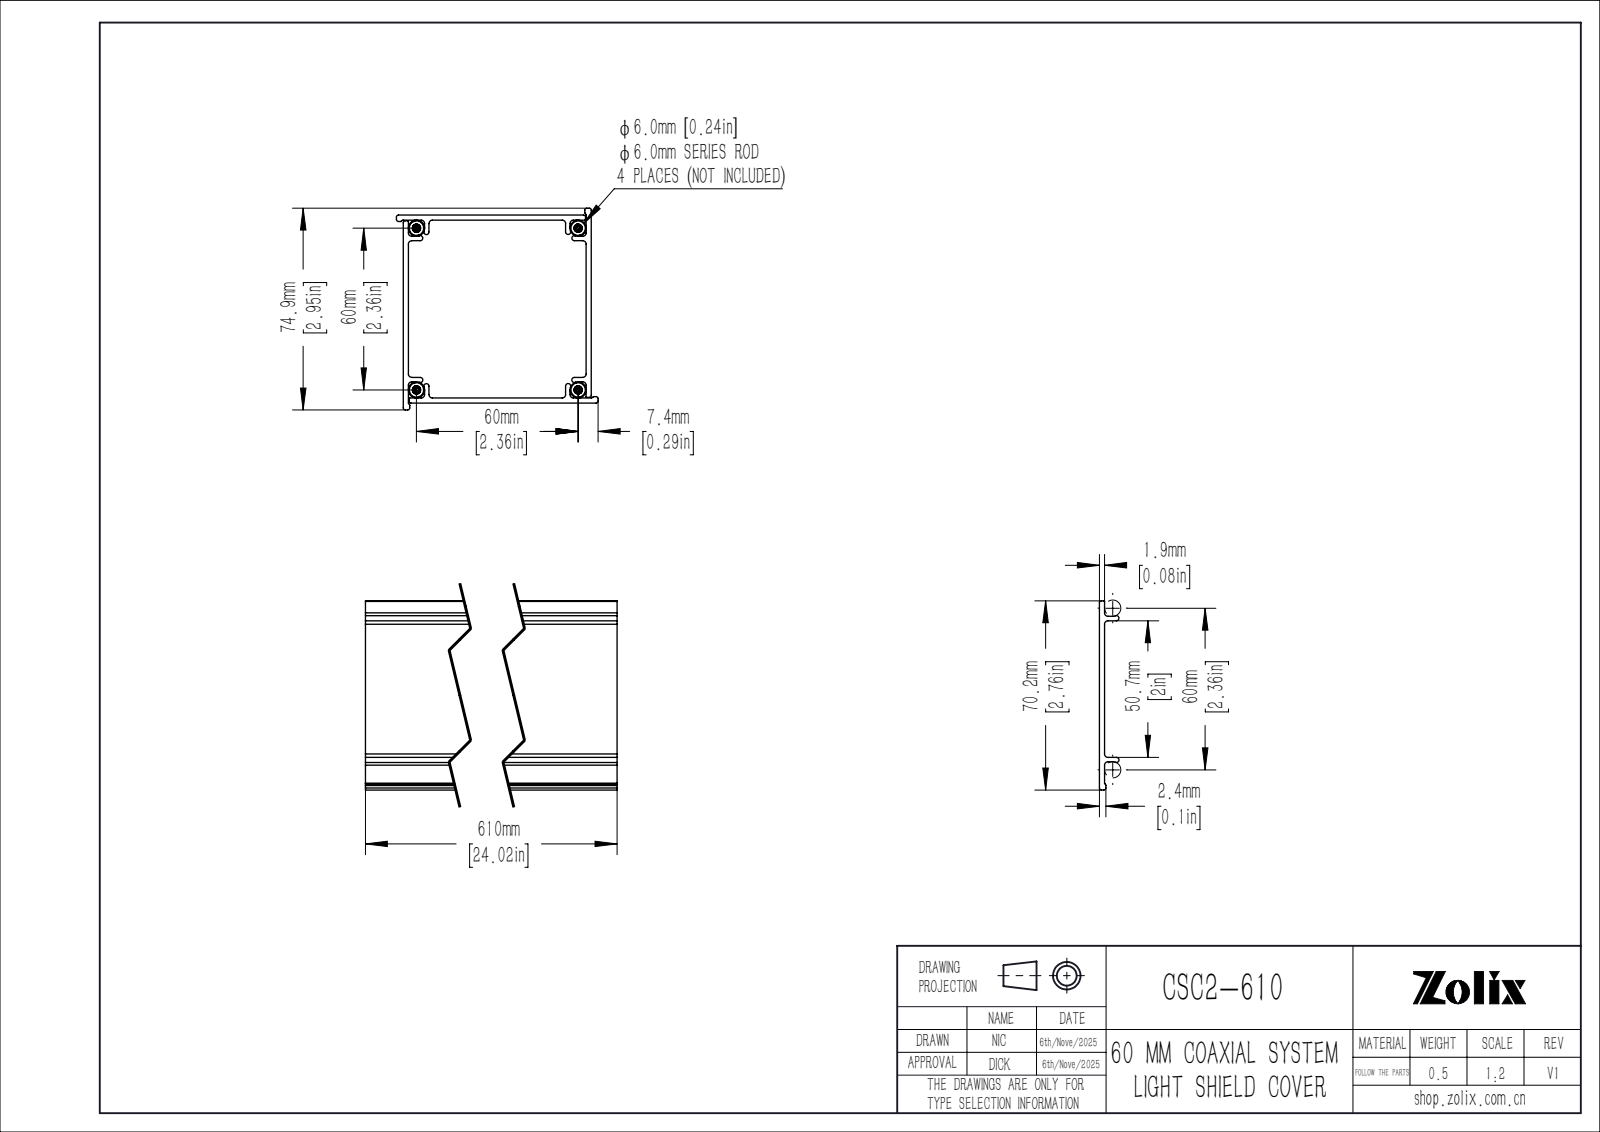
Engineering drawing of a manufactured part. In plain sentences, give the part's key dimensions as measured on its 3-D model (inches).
The part is named "GB_uT 80-2007[__________________M3__6]_M3__6.step; MOP-100-1.step; STEP模型-MOP-100-P4.step; CSSC2-610 (+1 more)". Its 3-D file was written by "SolidWorks 2020 (CONFIG_CONTROL_DESIGN)". It is 16 solids with 404 faces: 168 planar, 108 cylindrical and 128 other. Overall it measures 24.134 by 2.948 by 2.948 inches. Its volume is 23.54 cubic inches and its surface area 627.6 square inches. Round holes: 4 of diameter 0.098. Round bosses or shafts: 4 of diameter 0.236, 4 of diameter 0.118. Partial cylindrical surfaces (rounded edges, fillets, slot ends): 16 of radius 0.05, 12 of radius 0.01, 12 of radius 0.03, 8 of radius 0.037. The main face-to-face distances are 2.748, 0.075, 2.673, 2.598, 2.674, 0.075, 2.372, 0.301, 2.297, 0.376. The hole center spacings are 2.362, 3.341.
